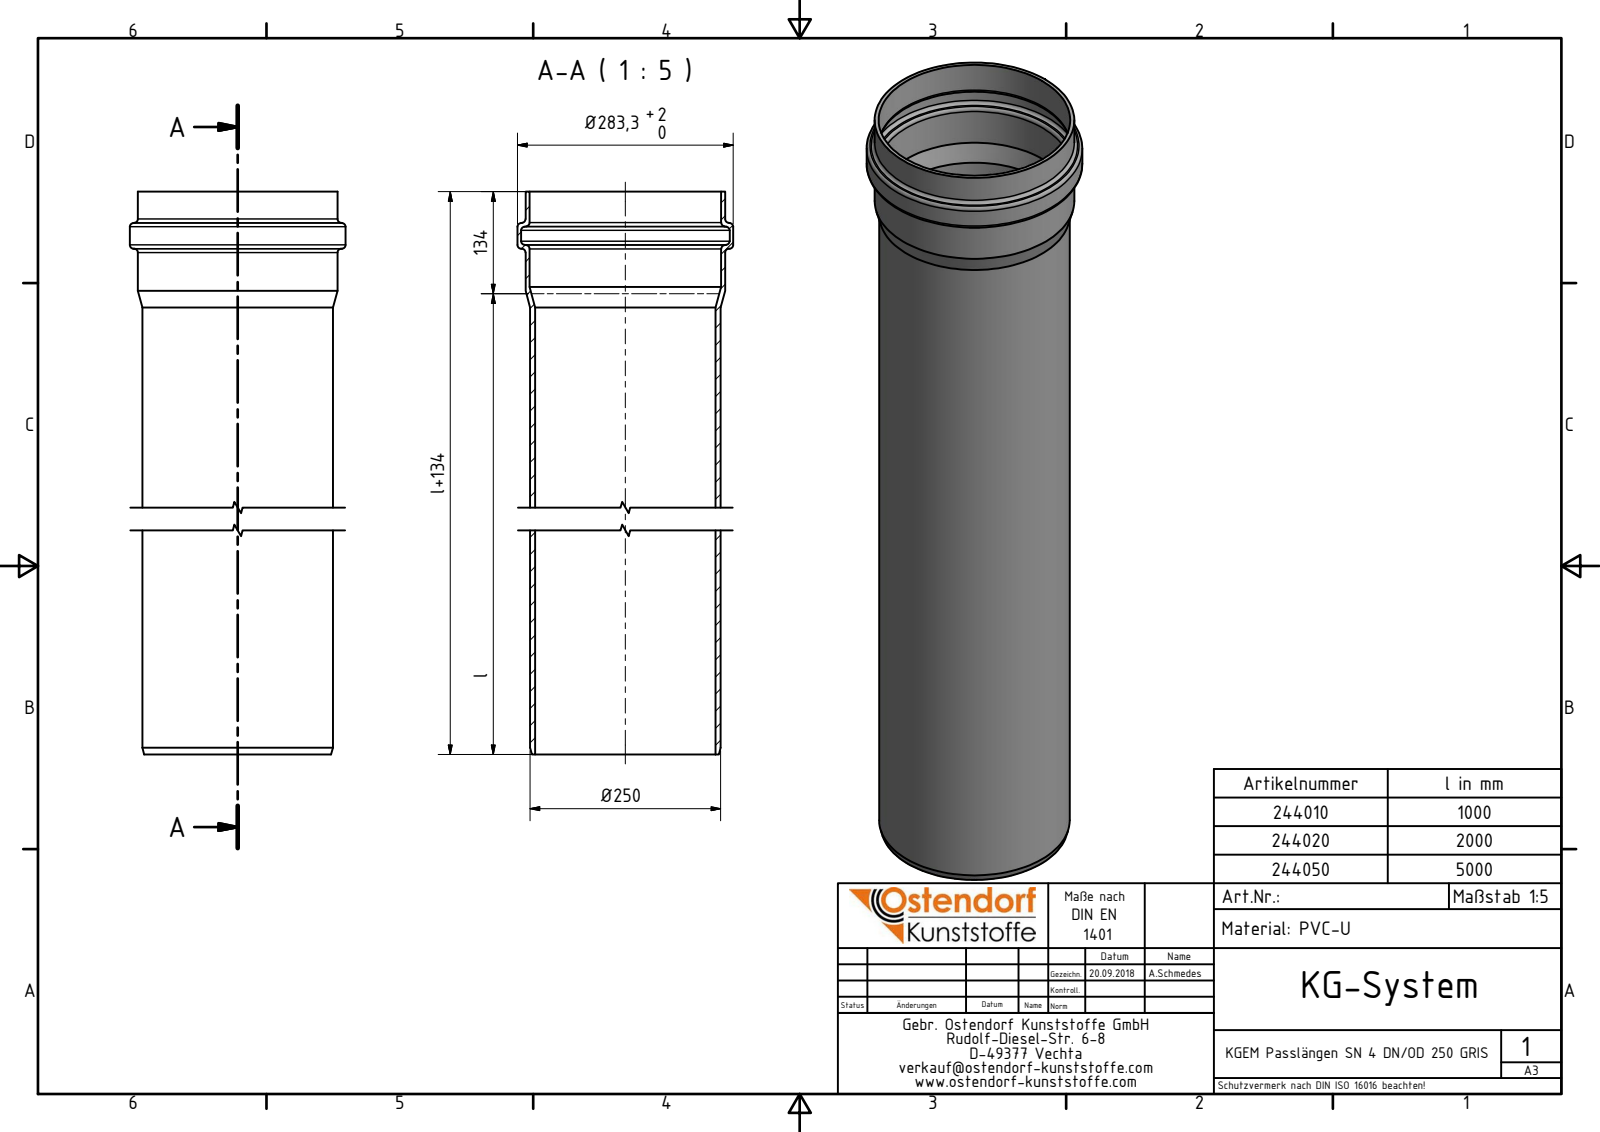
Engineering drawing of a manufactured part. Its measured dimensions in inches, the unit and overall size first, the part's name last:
Units: inches
Overall size (bounding box): 202.126 × 11.154 × 11.154
Round holes (diameter × count): ⌀9.329 ×1, ⌀9.902 ×1, ⌀10.783 ×1
Round bosses / shafts (diameter × count): ⌀11.154 ×1, ⌀10.319 ×1, ⌀9.852 ×1
Main face-to-face distances: 202.126
Volume: 1 593 in³ · Surface area: 12 250 in²
Bodies: 1 solid, 25 faces (2 planar, 8 cylindrical, 15 other)
Part name (STEP PRODUCT): 244050 KGEM Passlängen SN 4 DN_OD 250x5000 GRIS
STEP written by: Autodesk Inventor 2016 (AUTOMOTIVE_DESIGN)
